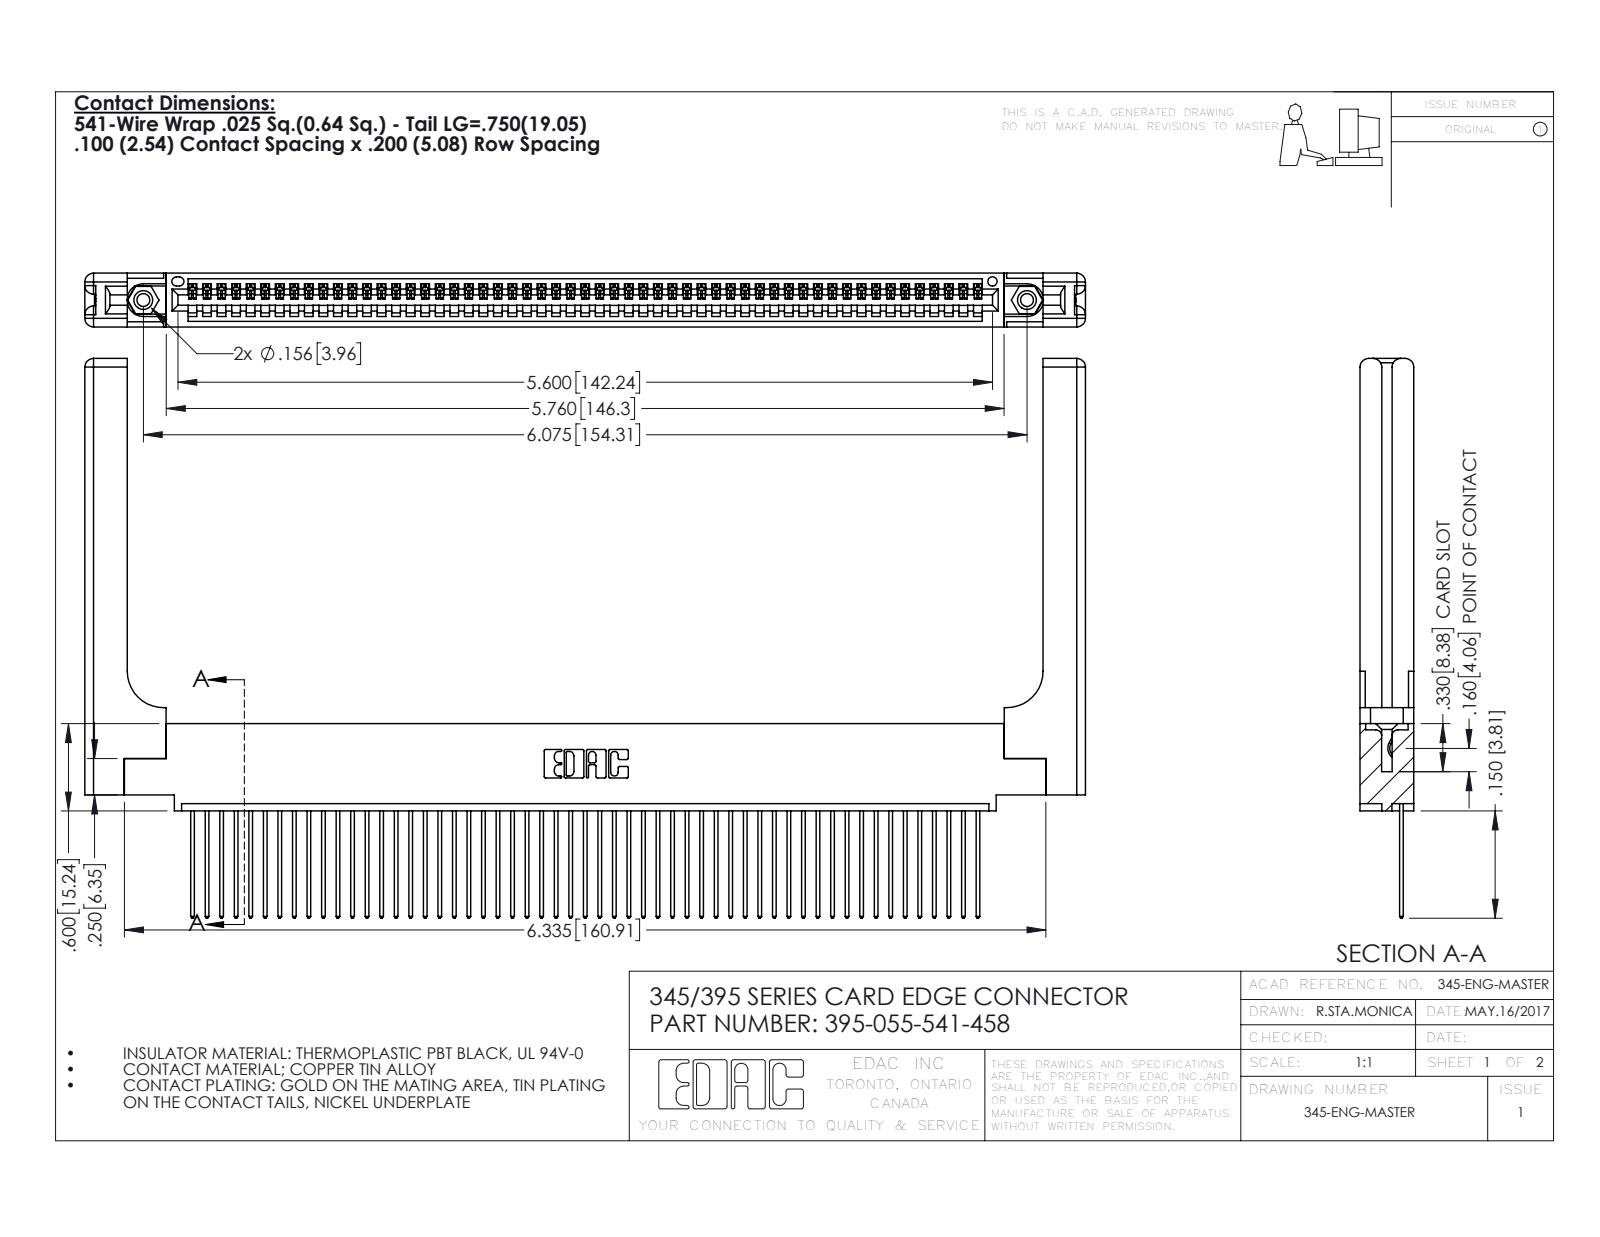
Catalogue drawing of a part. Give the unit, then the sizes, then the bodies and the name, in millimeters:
Units: millimetres
Overall size (bounding box): 174.7 × 97.7 × 9.4
Round holes (diameter × count): ⌀2.3 ×2, ⌀3.2 ×2, ⌀4 ×2, ⌀1.6 ×1
Round bosses / shafts (diameter × count): ⌀3.9 ×2
Partial cylindrical surfaces — rounded edges, fillets, slot ends (radius × count): R0.2 ×110, R0.3 ×110, R0.3 ×22, R1.5 ×16, R0.2 ×6, R0.8 ×6, R0.7 ×3, R0.8 ×2
Main face-to-face distances: 1.8, 7.6, 9.4, 2.5, 6.9, 0.6, 5.1, 5.7, 3.8, 3.8
Hole centre spacings: 6.9, 148.3, 154.3
Volume: 25 320 mm³ · Surface area: 28 970 mm²
Bodies: 60 solids, 3576 faces (2432 planar, 1084 cylindrical, 60 other)
Part name (STEP PRODUCT): 345-220-058_345-220-058; 345-250-001_345-250-001-102; 345-292-001_345-293-141; 345 Part_0.110 Offset - 0.156 Dia-TH (+1 more)
STEP written by: SolidWorks 2016 (CONFIG_CONTROL_DESIGN)
